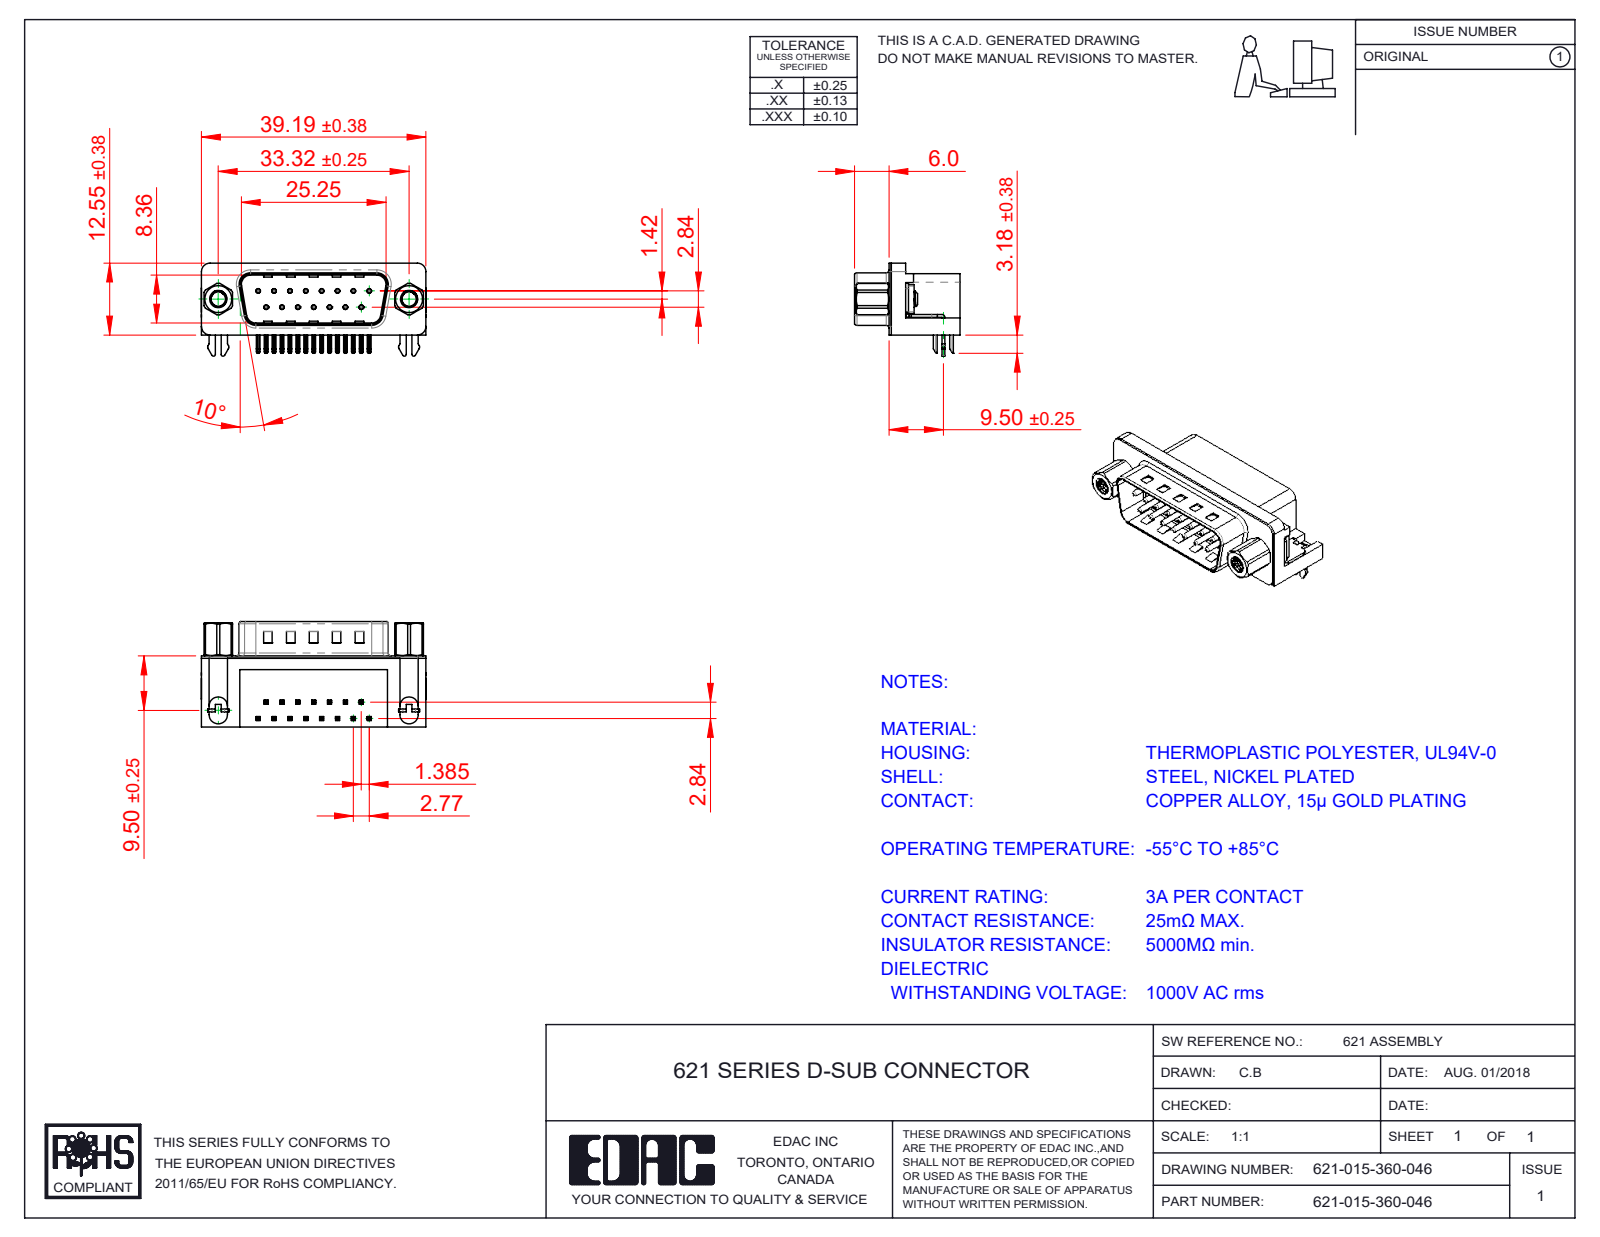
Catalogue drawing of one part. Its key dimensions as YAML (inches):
part_name: "621 M3 Threaded Rivet; 621 Contact Top; 621 Housing_15 Socket; 621 Contact Bottom (+4 more)"
step_written_by: "SolidWorks 2016 (CONFIG_CONTROL_DESIGN)"
units: inches
bodies: {solids: 23, faces: 1745, planar: 957, cylindrical: 547, other: 241}
overall_size: [1.544, 0.724, 0.64]
volume: 0.285
surface_area: 9.698
round_holes:
  - {diameter: 0.014, count: 15}
  - {diameter: 0.031, count: 15}
  - {diameter: 0.079, count: 2}
  - {diameter: 0.098, count: 2}
  - {diameter: 0.157, count: 2}
  - {diameter: 0.189, count: 2}
  - {diameter: 0.197, count: 2}
round_bosses_or_shafts:
  - {diameter: 0.03, count: 15}
  - {diameter: 0.118, count: 4}
  - {diameter: 0.193, count: 2}
  - {diameter: 0.187, count: 2}
  - {diameter: 0.154, count: 2}
partial_cylinders:
  - {radius: 0.01, count: 72}
  - {radius: 0.005, count: 30}
  - {radius: 0.039, count: 16}
  - {radius: 0.02, count: 9}
  - {radius: 0.063, count: 8}
  - {radius: 0.059, count: 6}
  - {radius: 0.035, count: 4}
  - {radius: 0.079, count: 4}
face_to_face_distances: [0.016, 0.472, 0.407, 0.488, 0.083, 0.412, 0.067, 0.428, 0.345, 0.374]
hole_center_spacings: [0.124, 0.109, 0.218, 0.327, 0.436, 0.198, 0.198, 0.294]
